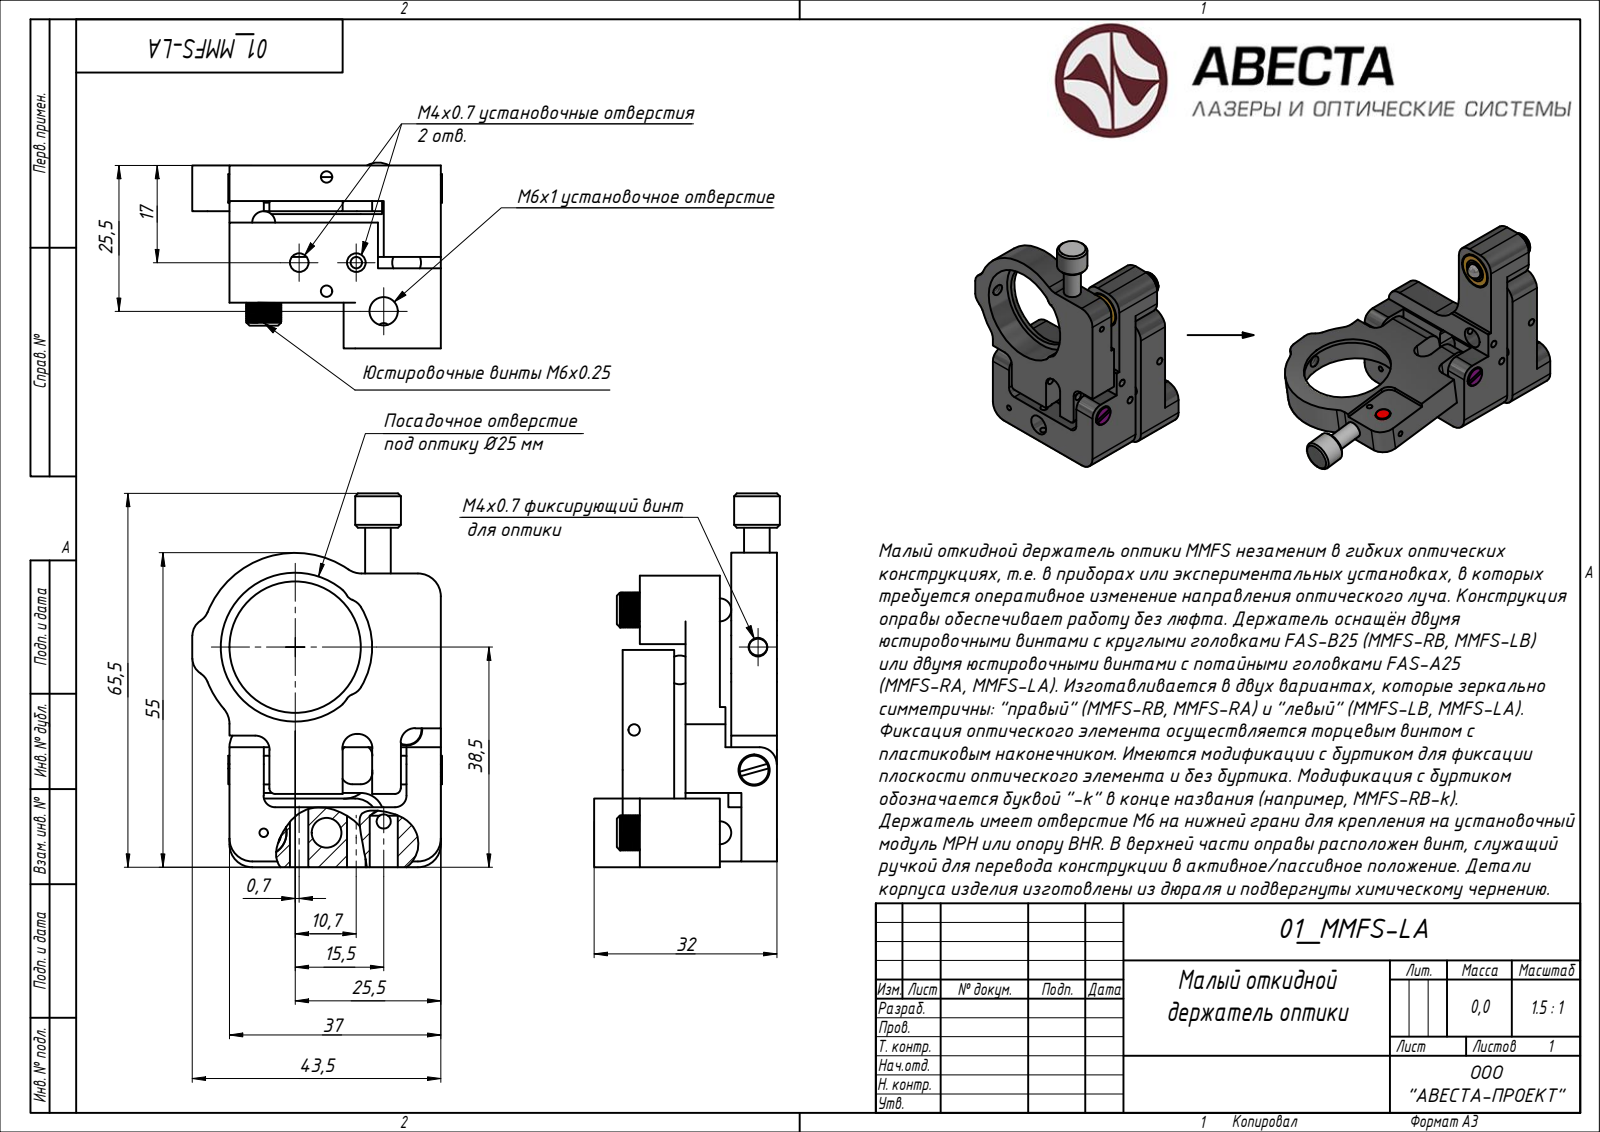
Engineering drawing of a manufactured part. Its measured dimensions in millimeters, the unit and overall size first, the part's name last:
Units: millimetres
Overall size (bounding box): 65.39 × 43.7 × 32.5
Main face-to-face distances: 8, 1, 2, 16, 12, 6, 10, 9, 11, 14
Volume: 25 231 mm³ · Surface area: 19 961 mm²
Bodies: 24 solids, 728 faces (158 planar, 0 cylindrical, 570 other)
STEP written by: ST-DEVELOPER v15 (AUTOMOTIVE_DESIGN)
